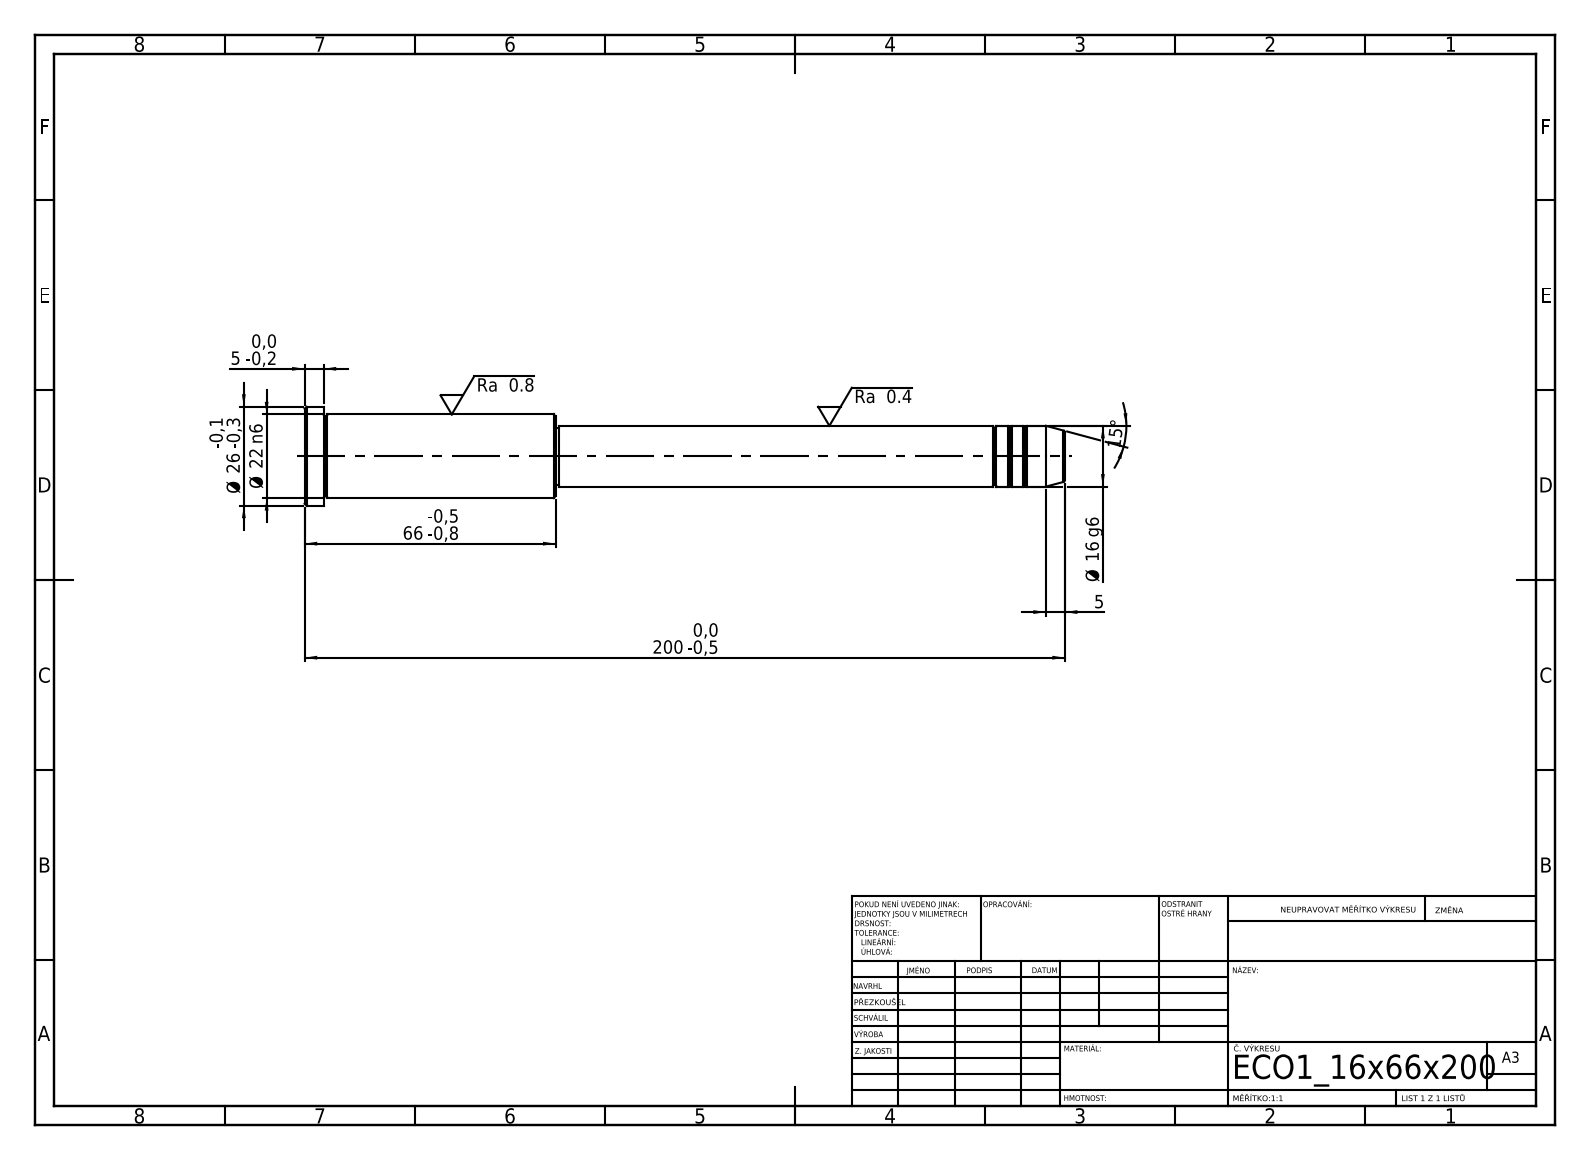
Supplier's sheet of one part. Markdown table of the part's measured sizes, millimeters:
| quantity | value |
| --- | --- |
| STEP written by | SolidWorks 2019 (CONFIG_CONTROL_DESIGN) |
| units | millimeters |
| bodies | 1 solid, 43 faces (5 planar, 14 cylindrical, 24 other) |
| overall size | 200 × 26 × 26 |
| volume | 52 498 mm³ |
| surface area | 12 456 mm² |
| round bosses / shafts (diameter × count) | 26 × 1, 22 × 1, 16 × 1, 15 × 1 |
| main face-to-face distances | 66, 61, 5, 134, 195, 200, 133, 1, 62, 67 |
